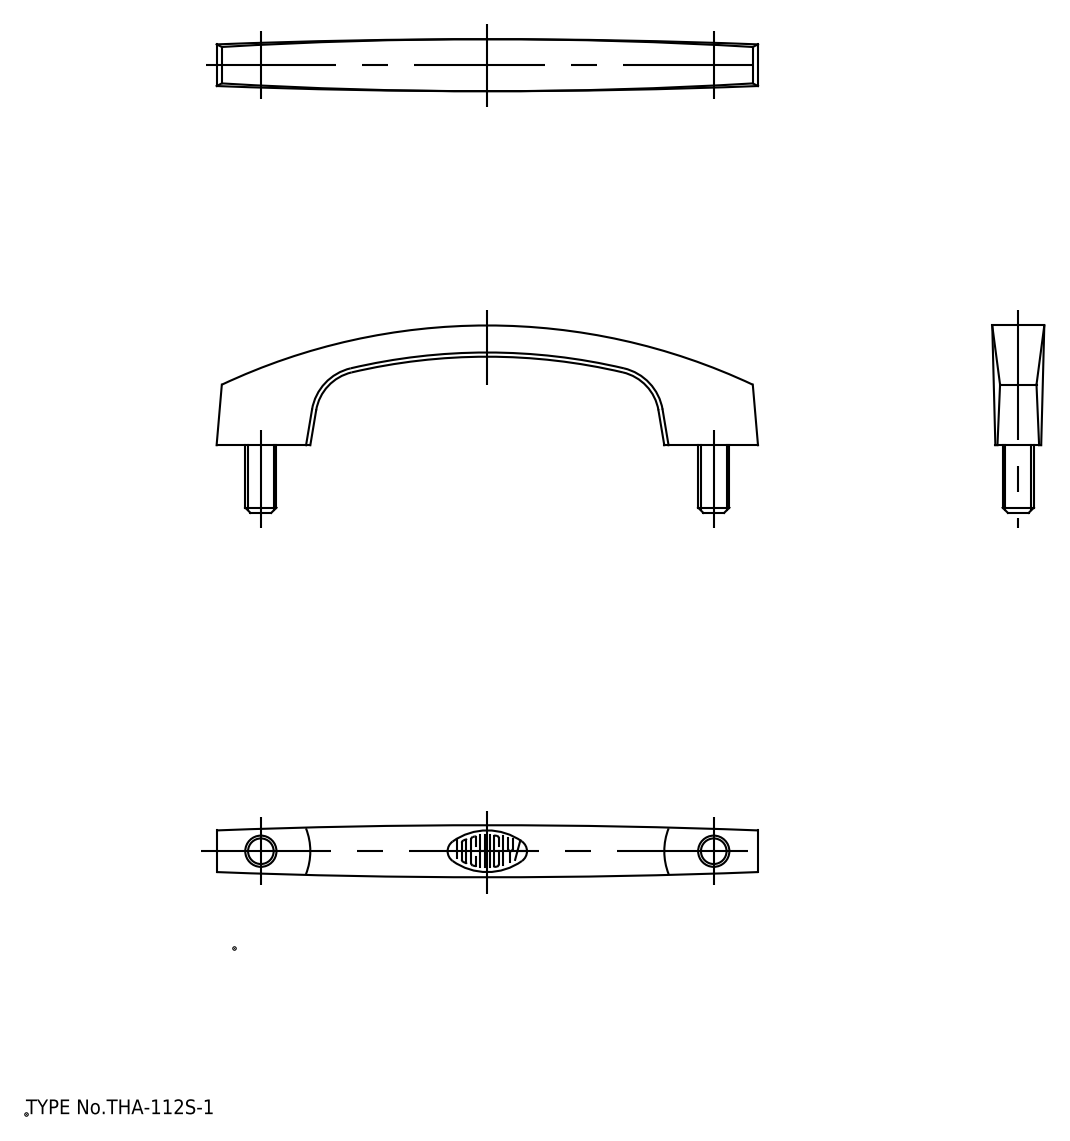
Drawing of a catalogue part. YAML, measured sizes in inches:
part_name: "screw; pull"
step_written_by: "spGate 19.8.4 (****-****-****-****) (AUTOMOTIVE_DESIGN)"
units: inches
bodies: {solids: 3, faces: 30, planar: 10, cylindrical: 11, other: 9}
overall_size: [4.094, 1.417, 0.394]
volume: 0.548
surface_area: 8.088
round_holes:
  - {diameter: 0.236, count: 2}
partial_cylinders:
  - {radius: 0.472, count: 2}
  - {radius: 4.724, count: 1}
face_to_face_distances: [0.315, 0.827, 0.512]
hole_center_spacings: [3.425]
